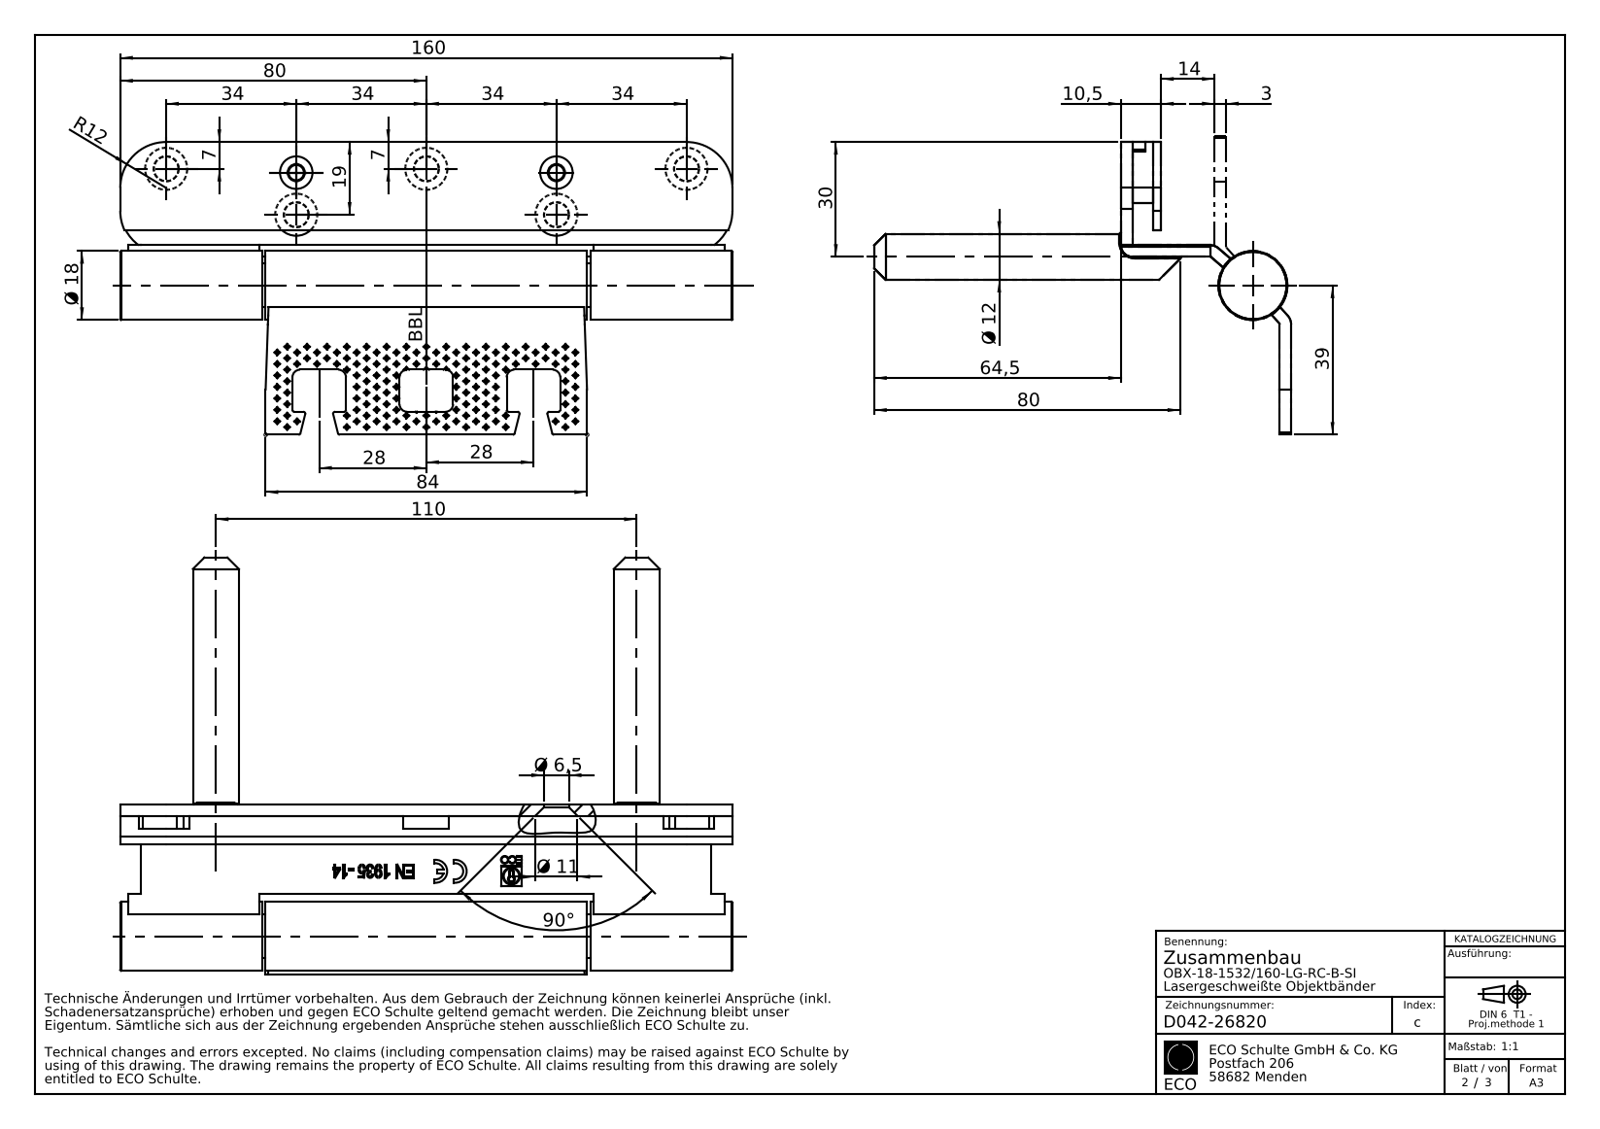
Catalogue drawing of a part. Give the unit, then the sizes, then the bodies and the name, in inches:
Units: inches
Overall size (bounding box): 6.299 × 4.252 × 1.89
Round holes (diameter × count): ⌀0.256 ×5, ⌀0.079 ×2, ⌀0.157 ×2, ⌀0.197 ×2, ⌀0.02 ×1, ⌀0.177 ×1, ⌀0.311 ×1
Round bosses / shafts (diameter × count): ⌀0.472 ×3, ⌀0.276 ×2, ⌀0.709 ×1, ⌀0.465 ×1, ⌀0.453 ×1, ⌀0.303 ×1, ⌀0.157 ×1, ⌀0.065 ×1
Partial cylindrical surfaces — rounded edges, fillets, slot ends (radius × count): R0.02 ×15, R0.079 ×8, R0.01 ×6, R0.138 ×6, R0.472 ×6, R0.004 ×4, R0.098 ×4, R0.027 ×2
Main face-to-face distances: 0.118, 0.079, 0.217, 0.335, 0.295, 0.965, 0.413, 0.551, 0.63, 0.157
Hole centre spacings: 1.339, 1.42, 2.677, 0.433, 2.712, 4.016, 4.043, 0.077
Volume: 6.064 in³ · Surface area: 96.05 in²
Bodies: 17 solids, 1938 faces (1630 planar, 185 cylindrical, 123 other)
Part name (STEP PRODUCT): D043-25252; OBX-18-1532-160-LG-RC-B-SI_D042-26820; D046-14312; D044-14308 (+8 more)
STEP written by: SolidWorks 2020 (CONFIG_CONTROL_DESIGN)
